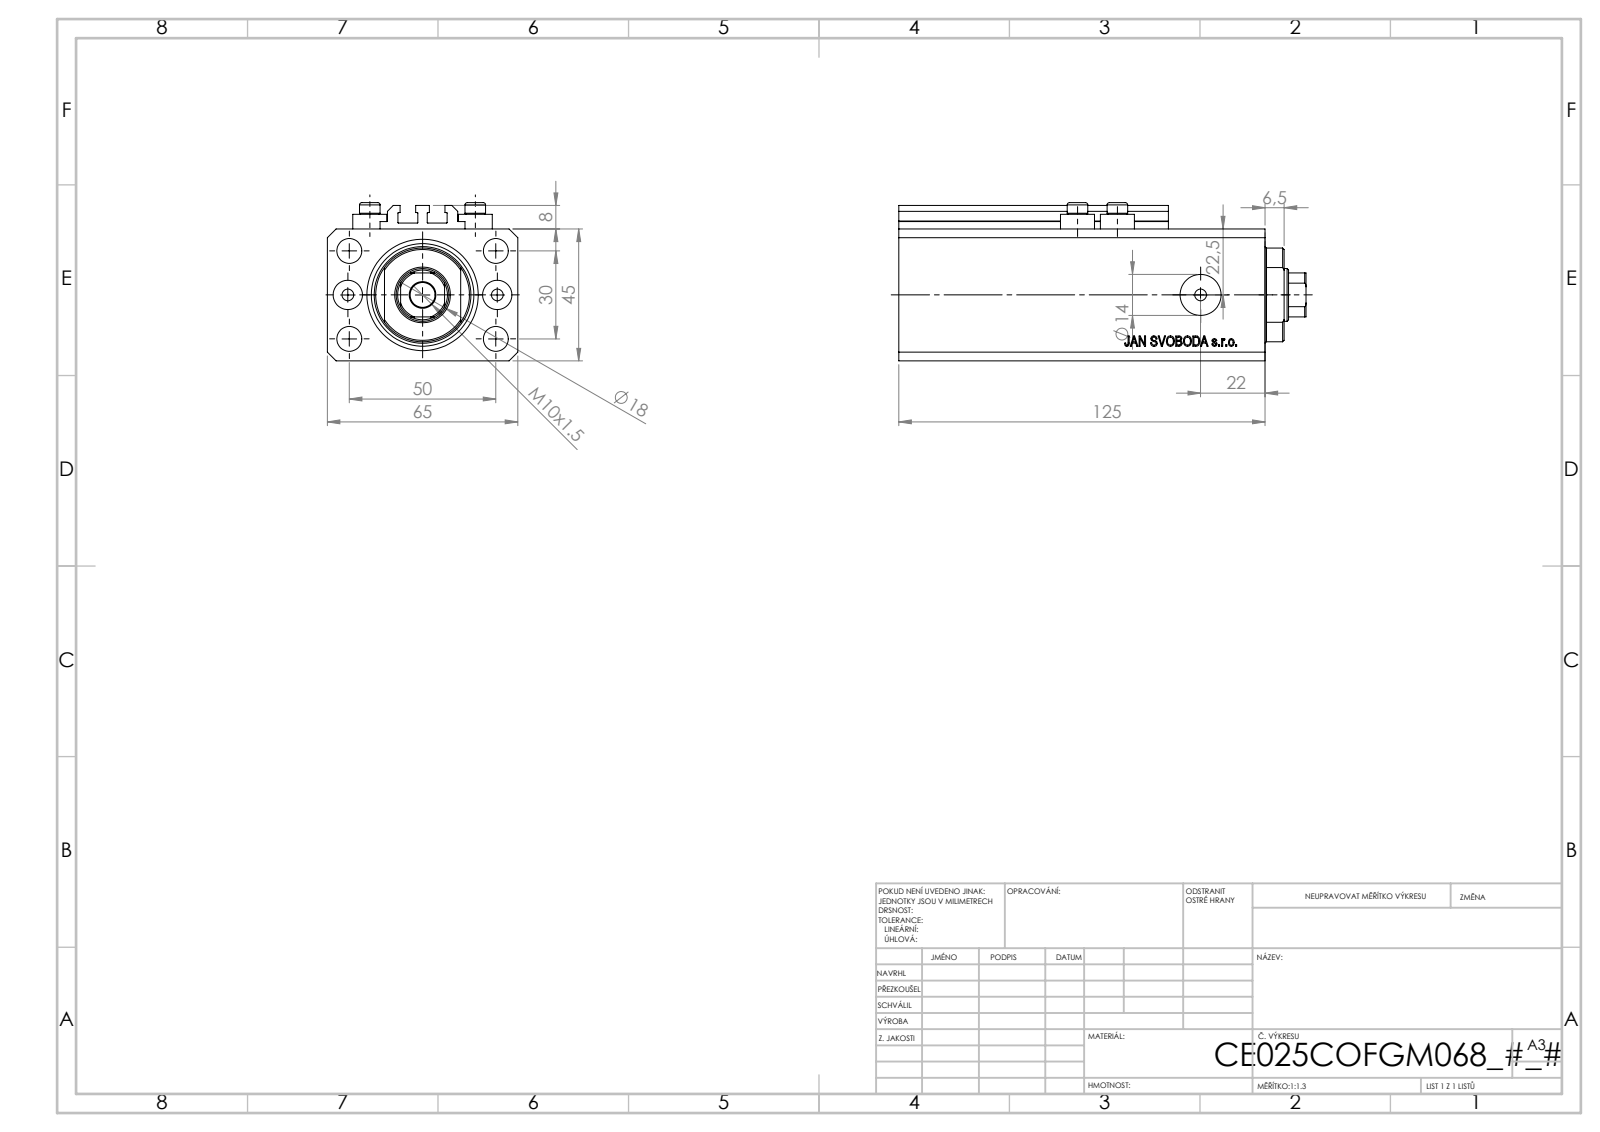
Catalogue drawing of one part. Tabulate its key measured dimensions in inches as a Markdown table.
| quantity | value |
| --- | --- |
| part name | ALLEN BOLT V250CE; V250CE_VC_C; V250CE_C_Body; V250CE_C_VCP |
| STEP written by | SolidWorks 2019 (CONFIG_CONTROL_DESIGN) |
| units | inches |
| bodies | 8 solids, 1034 faces (504 planar, 86 cylindrical, 444 other) |
| overall size | 5.472 × 2.559 × 2.126 |
| volume | 20.46 in³ |
| surface area | 130.1 in² |
| round holes (diameter × count) | 0.157 × 8, 0.335 × 5, 0.394 × 2, 0.551 × 2, 0.709 × 1, 0.984 × 1, 1.496 × 1 |
| round bosses / shafts (diameter × count) | 0.457 × 4, 0.276 × 4 |
| partial cylindrical surfaces (radius × count) | 0.008 × 10, 0.335 × 1, 0.63 × 1 |
| main face-to-face distances | 1.772, 2.559, 0.551, 1.85, 4.37, 4.921, 0.098, 0.079, 0.394, 0.807 |
| hole center spacings | 0.591, 1.148, 2.074, 0.535, 1.004, 1.181, 1.417, 1.515 |
